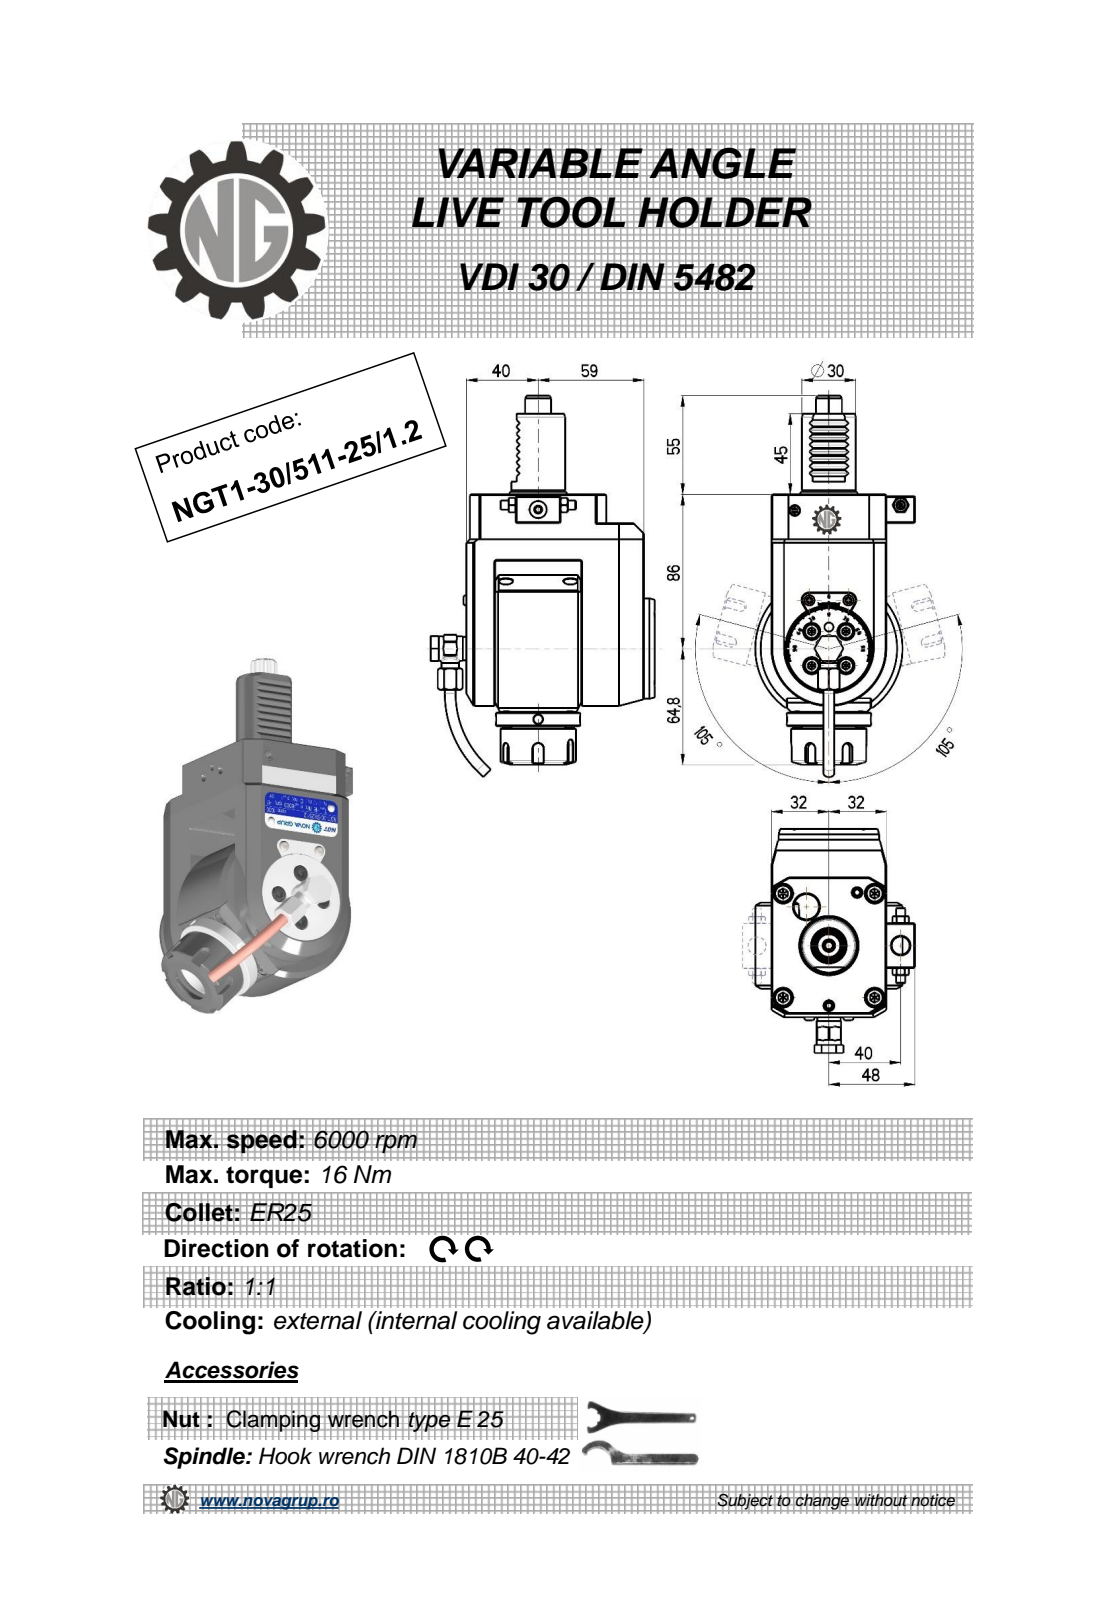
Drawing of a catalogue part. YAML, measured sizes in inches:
part_name: "NGT1_30_511_25_1_2"
step_written_by: "PRO/ENGINEER BY PARAMETRIC TECHNOLOGY CORPORATION, 2010280 (CONFIG_CONTROL_DESIGN)"
units: inches
bodies: {solids: 1, faces: 569, planar: 208, cylindrical: 160, other: 201}
overall_size: [8.373, 4.917, 3.504]
volume: 47.53
surface_area: 115.6
round_holes:
  - {diameter: 0.157, count: 3}
  - {diameter: 0.165, count: 2}
  - {diameter: 0.197, count: 2}
  - {diameter: 0.394, count: 2}
  - {diameter: 0.118, count: 1}
  - {diameter: 0.177, count: 1}
  - {diameter: 0.209, count: 1}
  - {diameter: 0.244, count: 1}
  - {diameter: 0.354, count: 1}
  - {diameter: 0.374, count: 1}
  - {diameter: 0.433, count: 1}
  - {diameter: 0.799, count: 1}
round_bosses_or_shafts:
  - {diameter: 0.236, count: 2}
  - {diameter: 0.224, count: 2}
  - {diameter: 3.228, count: 1}
  - {diameter: 2.205, count: 1}
  - {diameter: 1.85, count: 1}
  - {diameter: 1.654, count: 1}
  - {diameter: 1.378, count: 1}
  - {diameter: 1.181, count: 1}
partial_cylinders:
  - {radius: 0.115, count: 16}
  - {radius: 0.01, count: 12}
  - {radius: 0.012, count: 8}
  - {radius: 0.118, count: 5}
  - {radius: 0.02, count: 4}
  - {radius: 0.039, count: 2}
  - {radius: 0.226, count: 1}
  - {radius: 0.285, count: 1}
face_to_face_distances: [2.52, 0.63, 1.457, 0.236, 3.898, 4.134, 0.551, 0.827, 1.378, 1.614]
hole_center_spacings: [0.016, 1.553, 1.575, 1.929, 1.945, 2.49, 2.502, 3.521]
